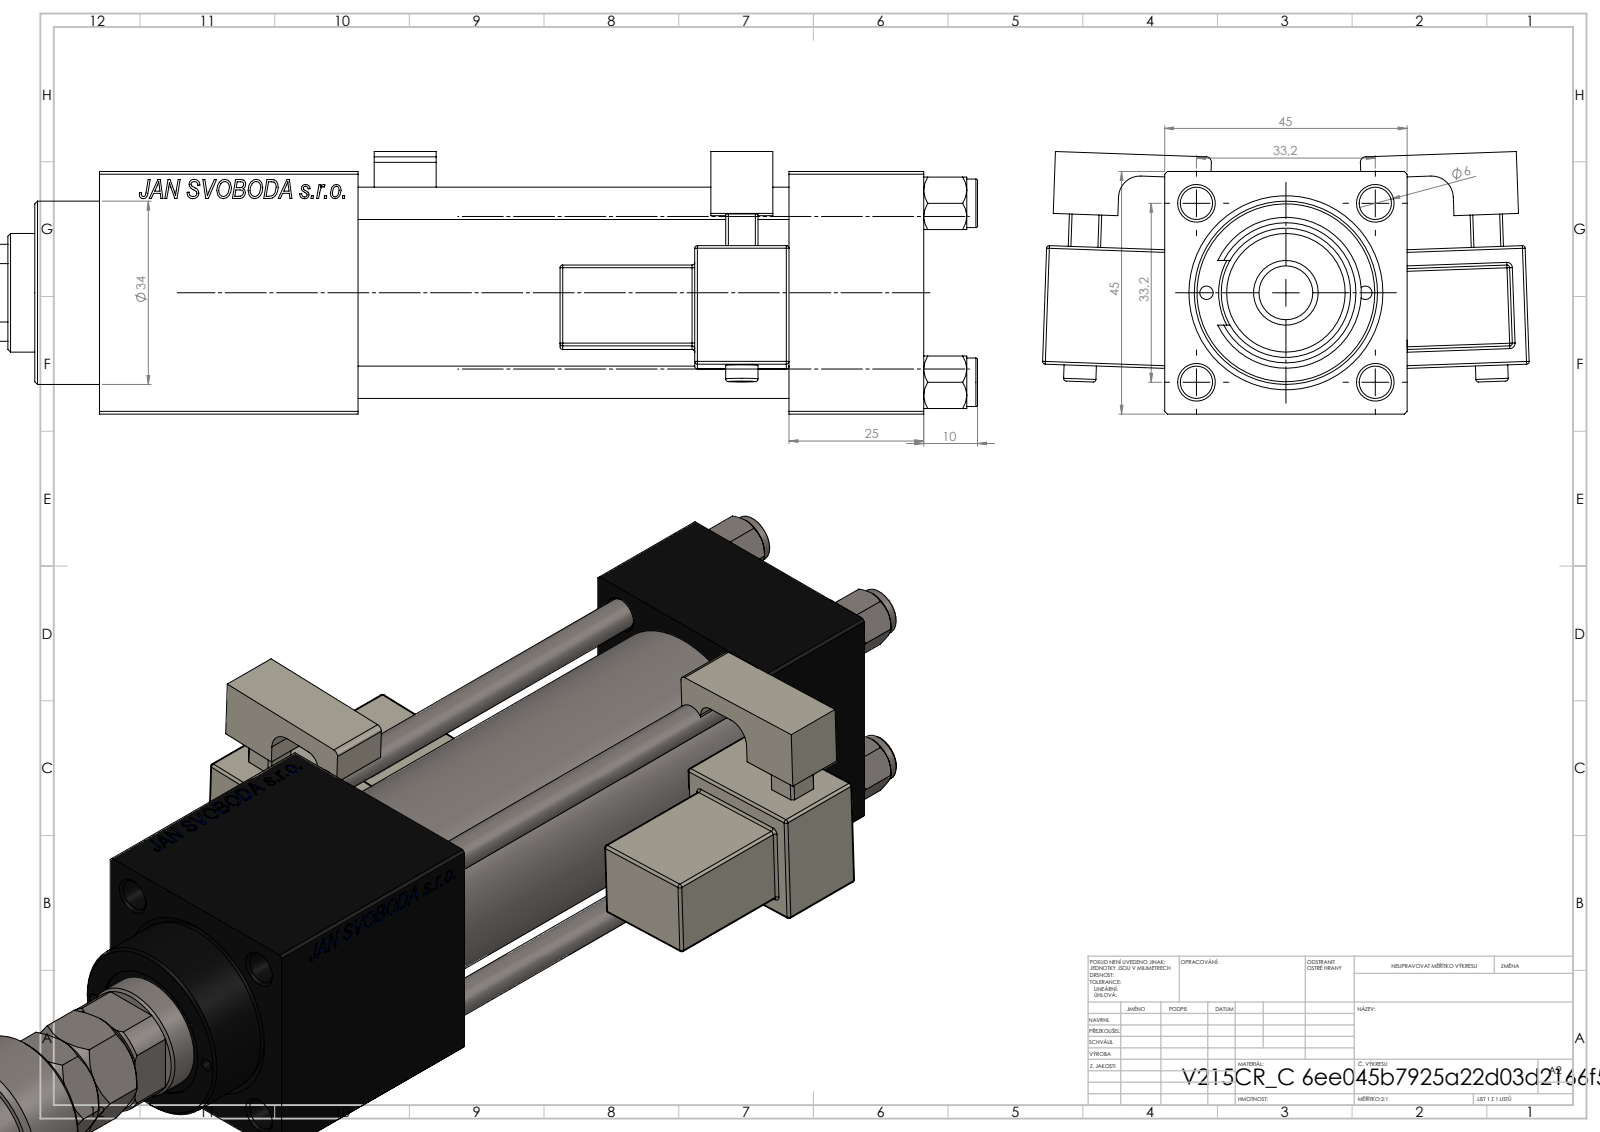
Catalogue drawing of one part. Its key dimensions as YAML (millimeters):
part_name: "V215CR_C_Body; V215CR_VCP_C; FEMALE_PART_FOR_DFA; NUT_M5_C (+4 more)"
step_written_by: "SolidWorks 2019 (CONFIG_CONTROL_DESIGN)"
units: millimeters
bodies: {solids: 15, faces: 1396, planar: 617, cylindrical: 163, other: 616}
overall_size: [249, 90.31, 48.72]
volume: 292923
surface_area: 101624
round_holes:
  - {diameter: 6, count: 4}
  - {diameter: 2.5, count: 2}
  - {diameter: 7, count: 2}
  - {diameter: 13.16, count: 2}
  - {diameter: 20, count: 2}
  - {diameter: 10.5, count: 1}
  - {diameter: 22, count: 1}
  - {diameter: 24, count: 1}
  - {diameter: 25, count: 1}
  - {diameter: 32, count: 1}
  - {diameter: 33, count: 1}
round_bosses_or_shafts:
  - {diameter: 9, count: 4}
  - {diameter: 6, count: 2}
  - {diameter: 38, count: 1}
  - {diameter: 34, count: 1}
  - {diameter: 28, count: 1}
  - {diameter: 18, count: 1}
  - {diameter: 12, count: 1}
  - {diameter: 11, count: 1}
partial_cylinders:
  - {radius: 0.5, count: 48}
  - {radius: 1, count: 2}
  - {radius: 2.5, count: 2}
  - {radius: 4, count: 2}
  - {radius: 9.75, count: 1}
  - {radius: 10.5, count: 1}
face_to_face_distances: [45, 25, 3, 105, 80, 153, 22.99, 62.5, 48, 14.5]
hole_center_spacings: [16.7, 23.48, 33.2, 35.47, 14.75, 46.95, 29.5, 105.5]
